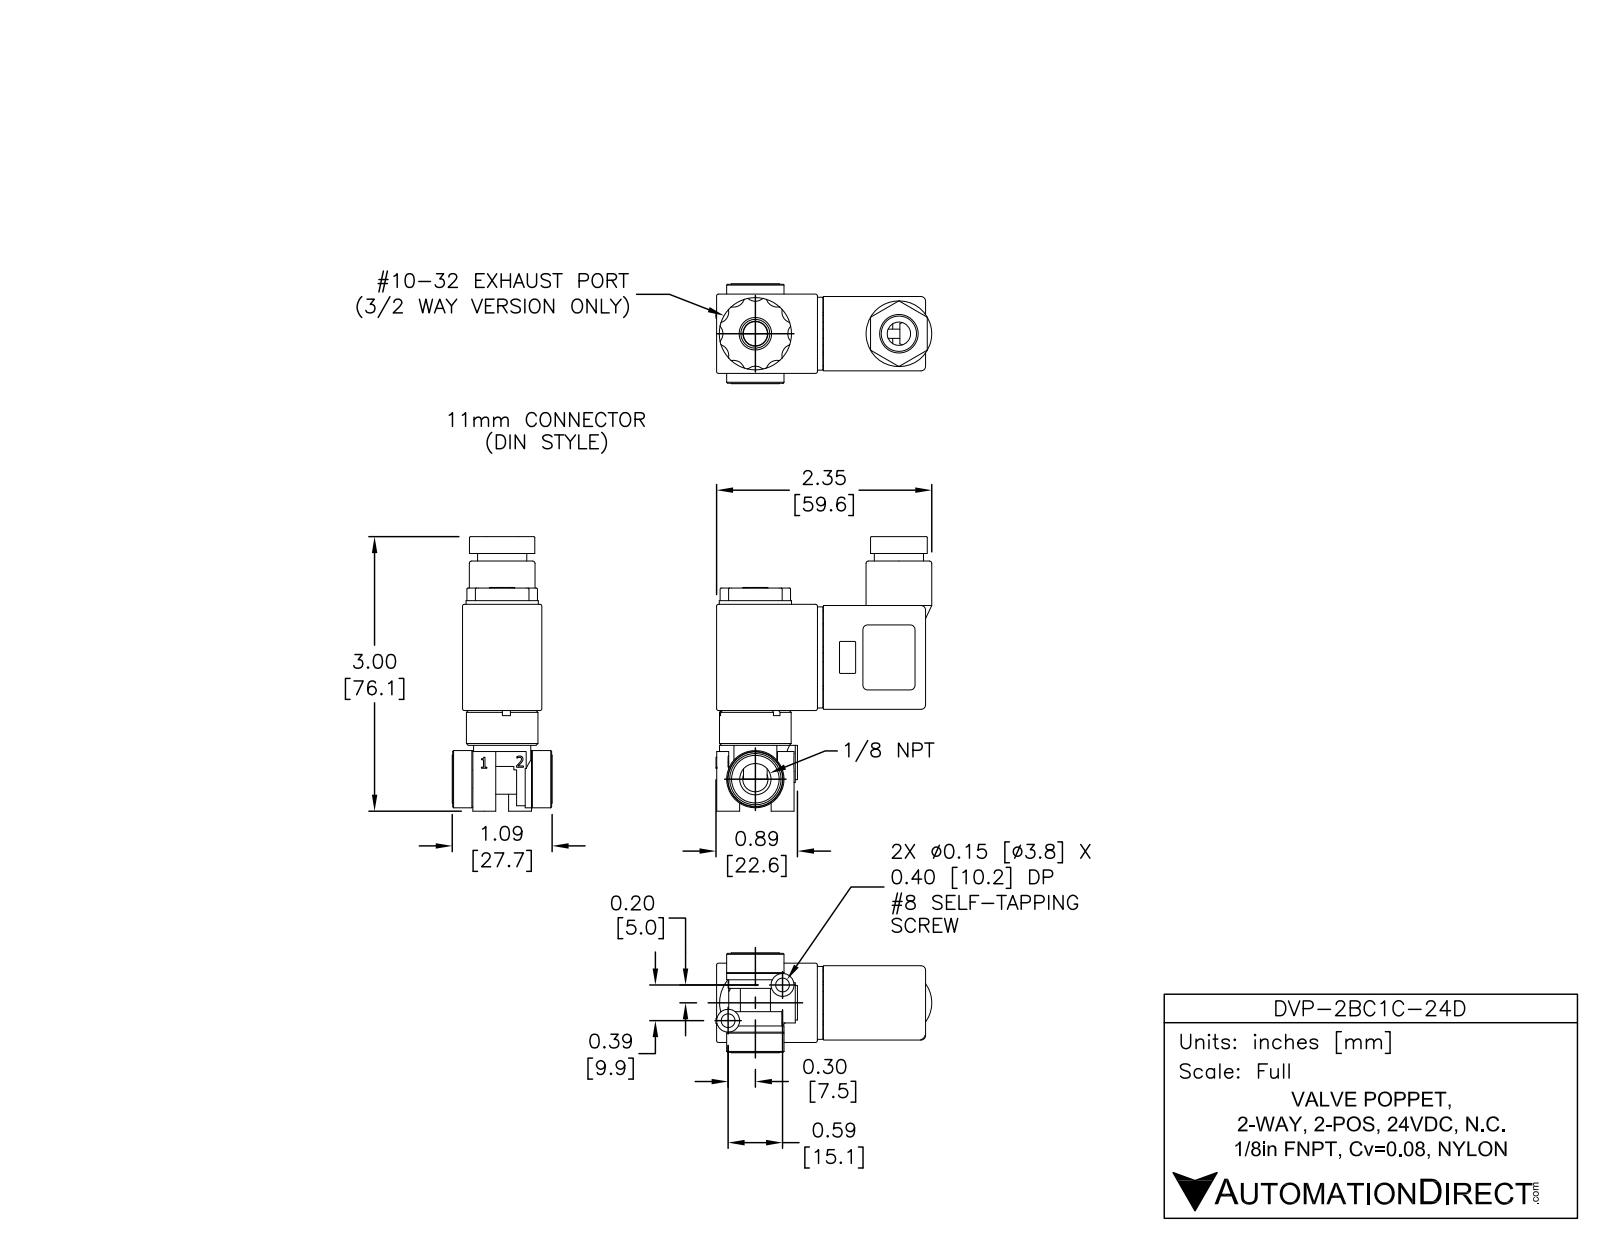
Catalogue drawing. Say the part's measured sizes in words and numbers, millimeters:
The part is named "DVP-2BC1C-24D". Its 3-D file was written by "SolidWorks 2015 (AUTOMOTIVE_DESIGN)". It is 4 solids with 1335 faces: 683 planar, 243 cylindrical and 409 other. Overall it measures 75.6 by 59.8 by 27.7 millimeters. Its volume is 32 400 cubic millimeters and its surface area 20 990 square millimeters. Round holes: 2 of diameter 2.5, 2 of diameter 3.2, 2 of diameter 3.8, 1 of diameter 1.6, 1 of diameter 2.6, 1 of diameter 4.2, 1 of diameter 5.2, 1 of diameter 6.8, 1 of diameter 6.9, 1 of diameter 7, 1 of diameter 7, 1 of diameter 8.2. Round bosses or shafts: 3 of diameter 6.4, 2 of diameter 15.9, 1 of diameter 20, 1 of diameter 19.8, 1 of diameter 18.2, 1 of diameter 15, 1 of diameter 14.2, 1 of diameter 13.7. Partial cylindrical surfaces (rounded edges, fillets, slot ends): 46 of radius 0.3, 16 of radius 1.3, 12 of radius 0.5, 12 of radius 3.1, 3 of radius 1.1, 2 of radius 0.6, 2 of radius 0.6, 2 of radius 0.7. The main face-to-face distances are 1.5, 2.2, 19.8, 0.7, 21.3, 19.1, 22, 29.5, 0.9, 21.1. The hole center spacings are 9, 4.4, 5.8, 13, 14.5, 18, 18.4, 25.3.
